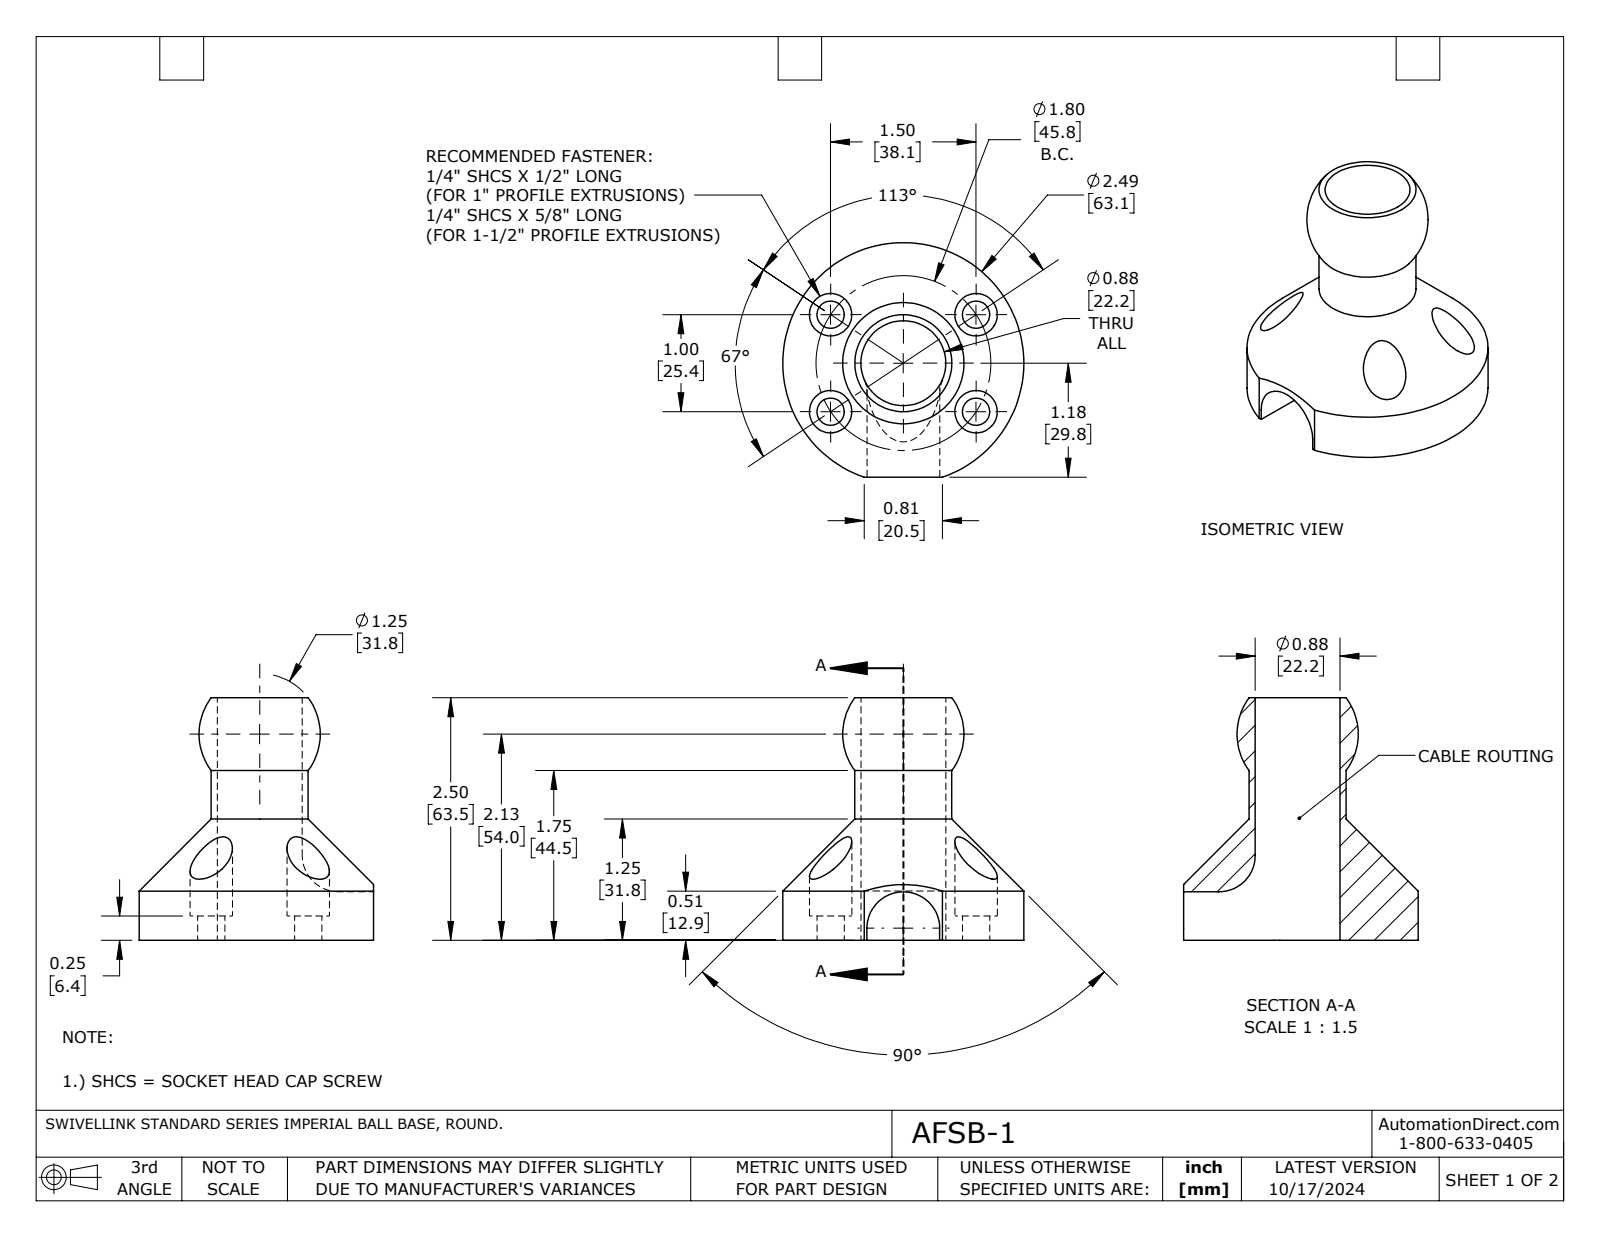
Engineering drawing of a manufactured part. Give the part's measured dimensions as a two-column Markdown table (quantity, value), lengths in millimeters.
| quantity | value |
| --- | --- |
| part name | AFSB-1 |
| STEP written by | SolidWorks 2021 (CONFIG_CONTROL_DESIGN) |
| units | millimeters |
| bodies | 1 solid, 24 faces (9 planar, 12 cylindrical, 3 other) |
| overall size | 64.2 × 63.1 × 61.4 |
| volume | 54 720 mm³ |
| surface area | 18 540 mm² |
| round holes (diameter × count) | 7.1 × 4, 11.1 × 4, 22.2 × 1 |
| round bosses / shafts (diameter × count) | 63.1 × 1, 25.4 × 1 |
| partial cylindrical surfaces (radius × count) | 9.5 × 1 |
| main face-to-face distances | 6.4, 57.2, 63.5, 19.1 |
| hole center spacings | 22.9, 25.4, 38.1, 45.8 |
